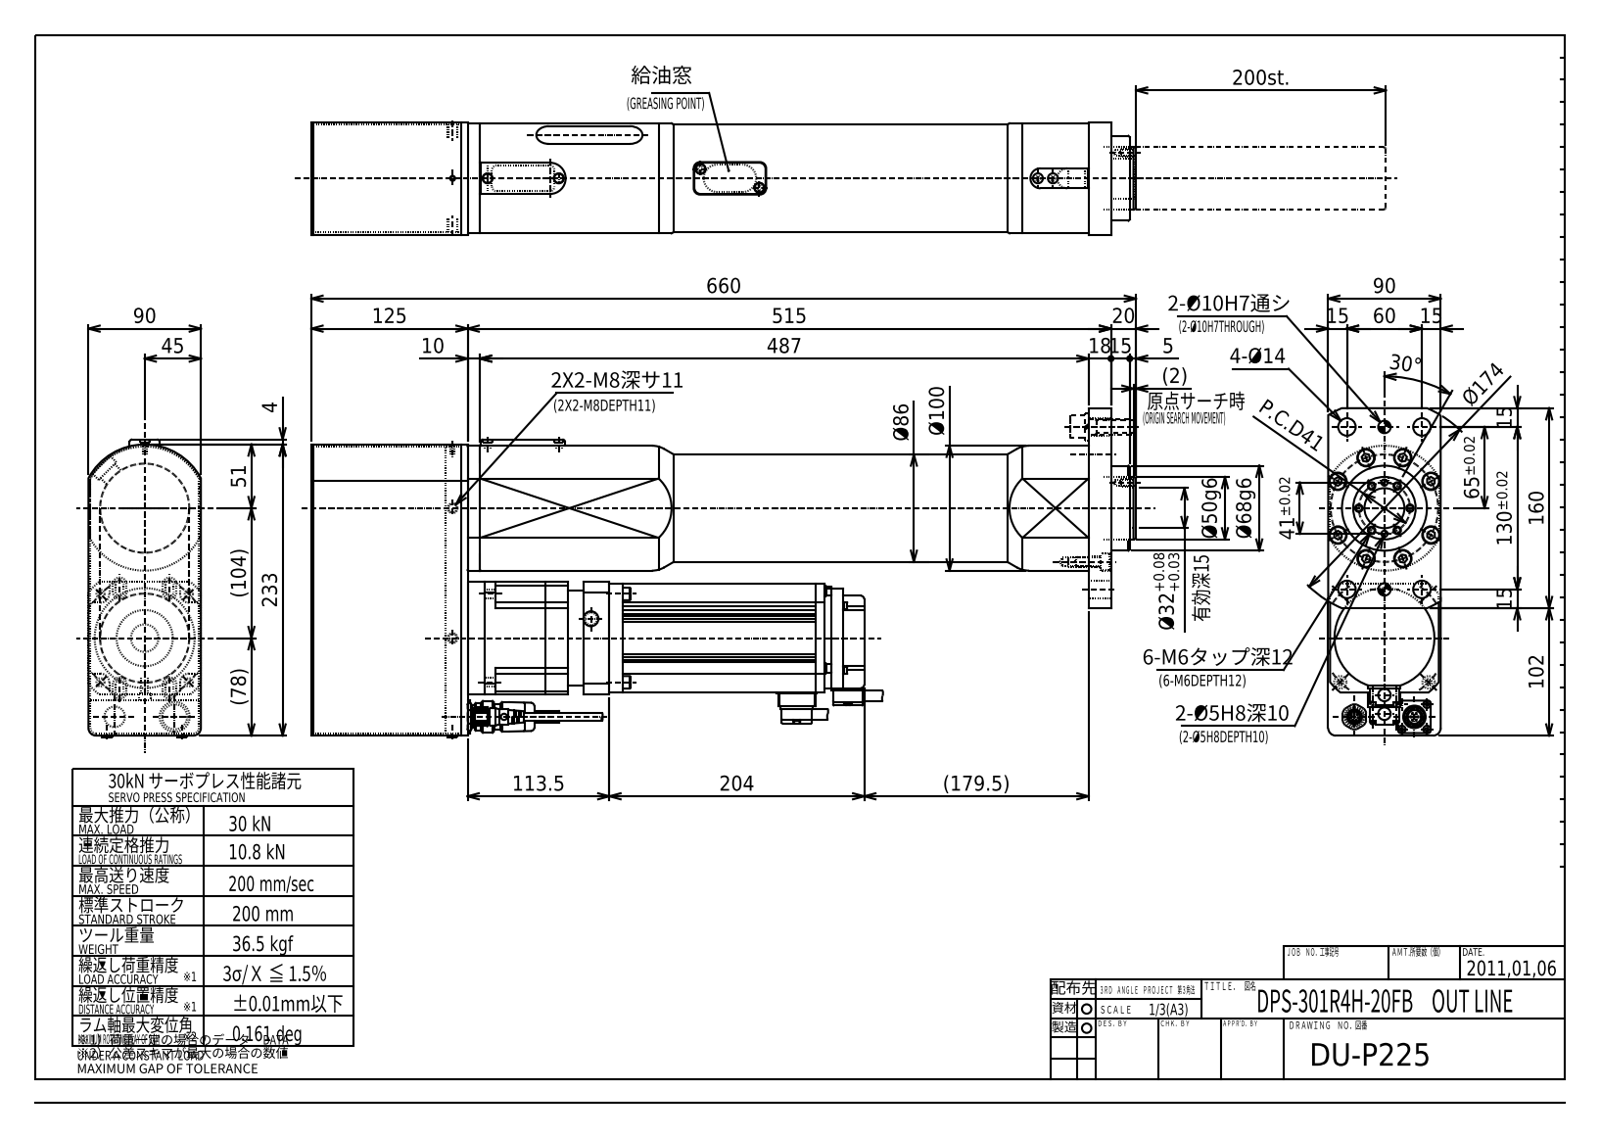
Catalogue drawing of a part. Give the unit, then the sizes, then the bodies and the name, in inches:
Units: inches
Overall size (bounding box): 25.984 × 10.472 × 3.543
Round holes (diameter × count): ⌀0.262 ×20, ⌀0.194 ×14, ⌀0.551 ×12, ⌀0.197 ×9, ⌀0.354 ×8, ⌀0.097 ×6, ⌀0.128 ×5, ⌀0.177 ×4, ⌀0.217 ×4, ⌀0.256 ×4, ⌀0.26 ×4, ⌀0.315 ×4
Round bosses / shafts (diameter × count): ⌀0.276 ×14, ⌀0.315 ×9, ⌀0.512 ×8, ⌀0.157 ×8, ⌀0.394 ×6, ⌀0.197 ×6, ⌀0.236 ×5, ⌀0.346 ×4
Partial cylindrical surfaces — rounded edges, fillets, slot ends (radius × count): R0.039 ×50, R0.079 ×32, R0.012 ×16, R0.02 ×14, R0.118 ×12, R0.197 ×12, R0.177 ×10, R0.128 ×8
Main face-to-face distances: 0.059, 3.543, 0.039, 3.484, 3.504, 3.445, 0.02, 0.079, 0.118, 0.591
Hole centre spacings: 1.693, 3.182, 0.557, 0.787, 1.128, 1.14, 1.158, 1.181
Volume: 483.2 in³ · Surface area: 1 020 in²
Bodies: 3 solids, 1736 faces (883 planar, 560 cylindrical, 293 other)
Part name (STEP PRODUCT): DU-P00-710+C_OUTLINE; DPS-301R4H-20FB(DU-P225+I)_OUTLINE; DPS-301R4H-20FB(DU-P225+I)_OUTLINE.
STEP written by: Autodesk Inventor 2015 (AUTOMOTIVE_DESIGN)
